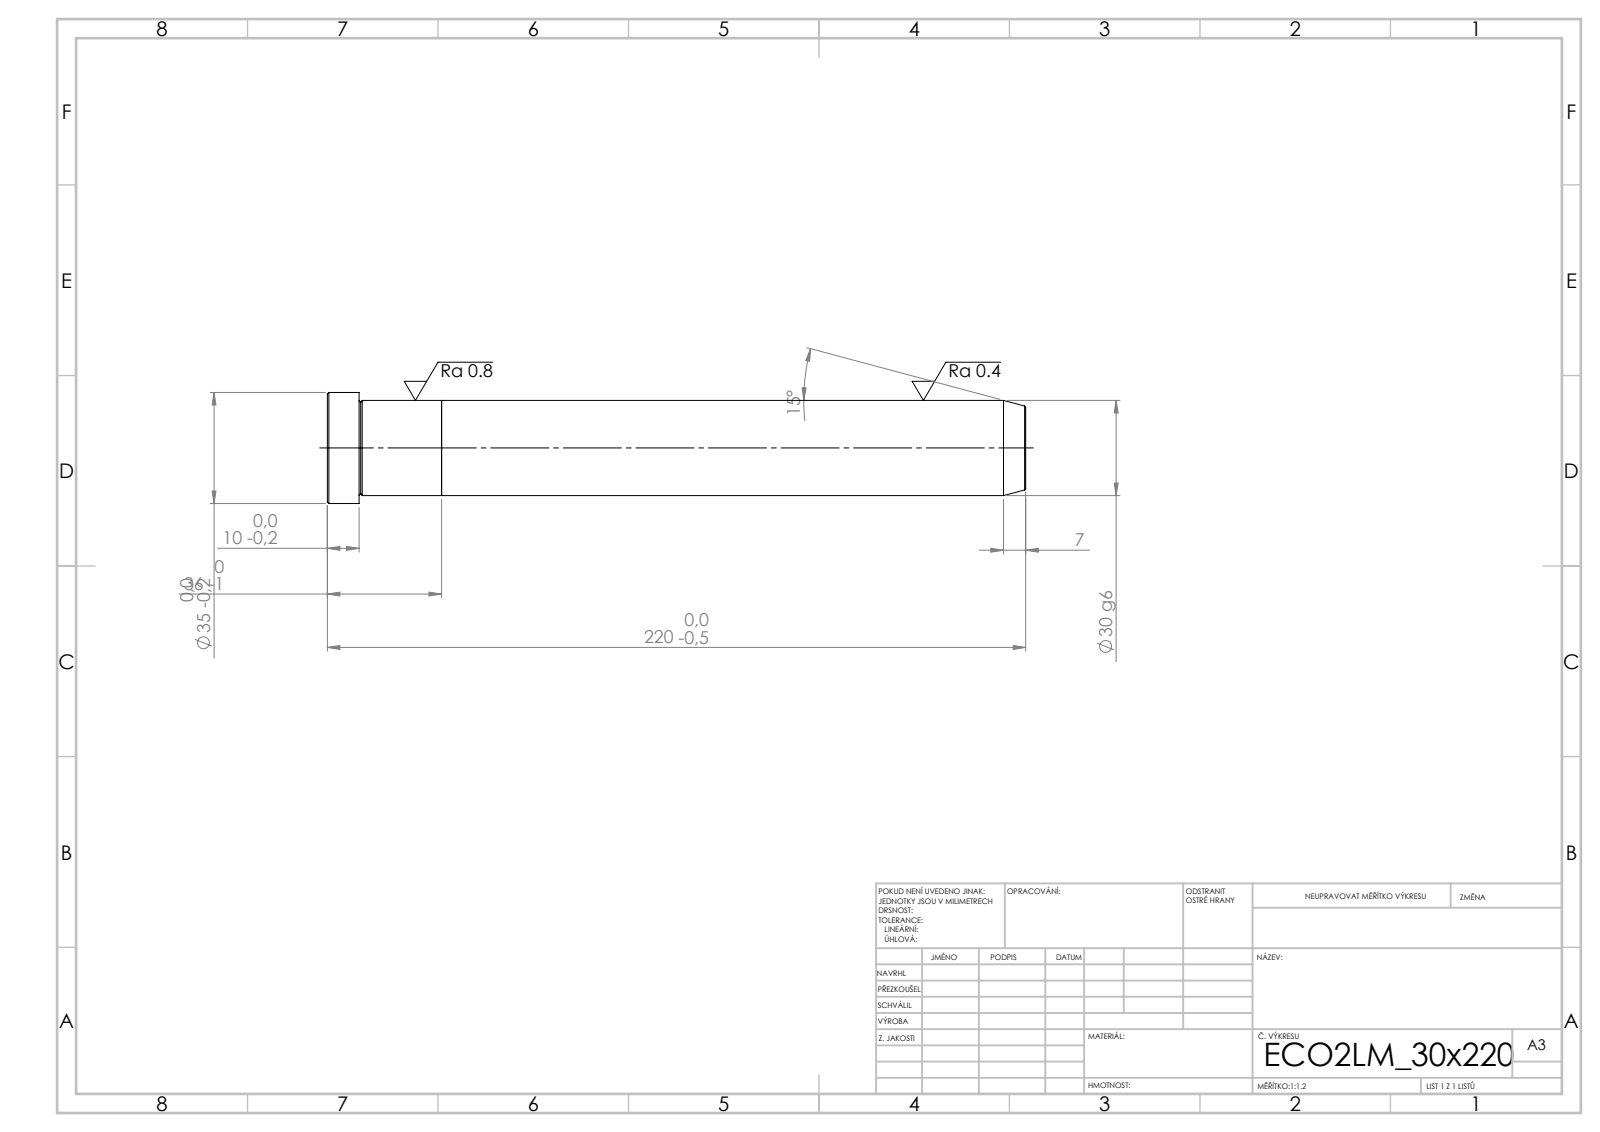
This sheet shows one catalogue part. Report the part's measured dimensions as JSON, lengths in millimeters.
{"step_written_by": "SolidWorks 2019 (CONFIG_CONTROL_DESIGN)", "units": "millimeters", "bodies": {"solids": 2, "faces": 21, "planar": 5, "cylindrical": 6, "other": 10}, "overall_size": [220, 35, 35], "volume_mm3": 157416, "surface_area_mm2": 24053, "round_bosses_or_shafts": [[35, 1], [30, 1]], "face_to_face_distances": [36, 184, 220, 210, 26, 10]}
